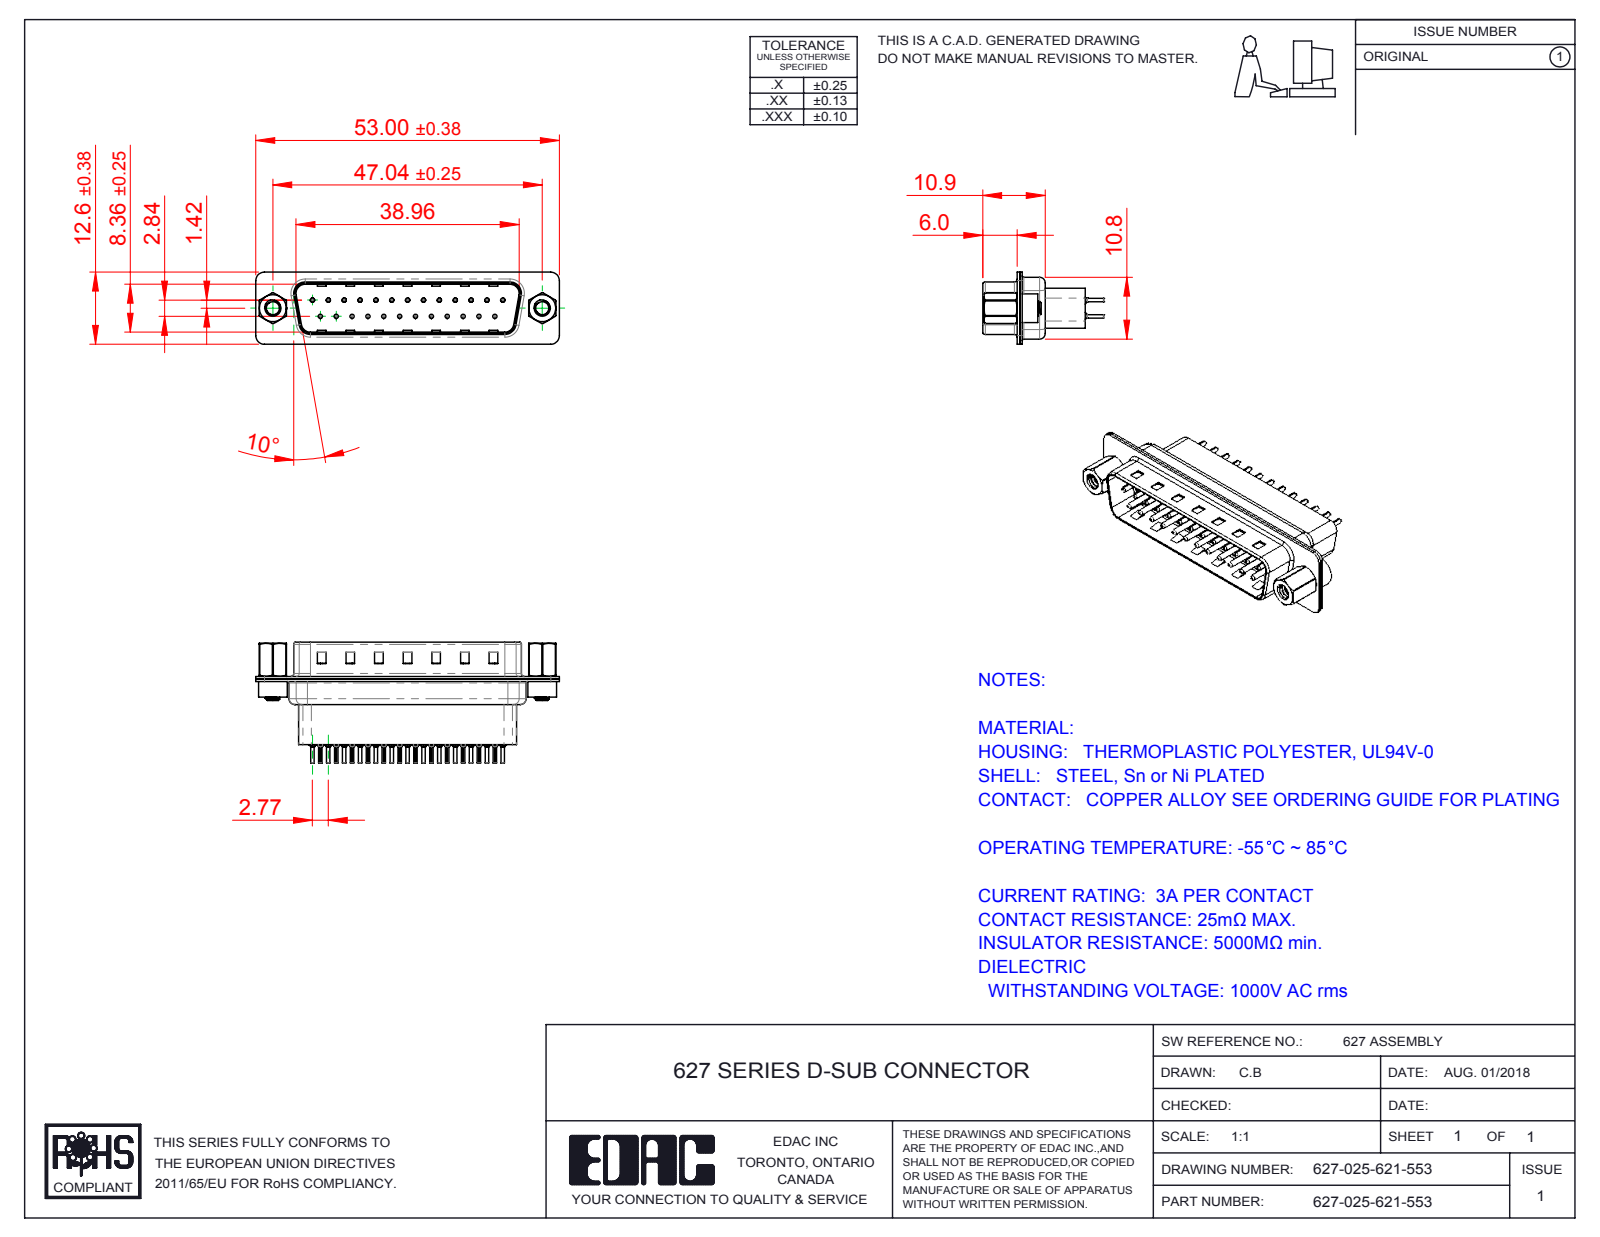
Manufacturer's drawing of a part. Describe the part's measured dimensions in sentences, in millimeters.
The part is named "627 Shell Rear_25 Contacts; 627 Contact Row 1_21H; 627 4-40 Threaded Rivet; 627 Housing_25 HP (+4 more)". Its 3-D file was written by "SolidWorks 2016 (CONFIG_CONTROL_DESIGN)". It is 32 solids with 2952 faces: 793 planar, 1134 cylindrical and 1025 other. Overall it measures 53 by 21.1 by 12.6 millimeters. Its volume is 4 126 cubic millimeters and its surface area 10 464 square millimeters. Round holes: 25 of diameter 0.2, 25 of diameter 0.35, 25 of diameter 1.1, 25 of diameter 1.6, 2 of diameter 2.26, 2 of diameter 2.29, 2 of diameter 4, 2 of diameter 4.8. Round bosses or shafts: 25 of diameter 2, 25 of diameter 1.5, 25 of diameter 0.75, 25 of diameter 0.6, 2 of diameter 5, 2 of diameter 4.9, 2 of diameter 2.79. Partial cylindrical surfaces (rounded edges, fillets, slot ends): 50 of radius 0.1, 16 of radius 1.5, 12 of radius 2, 8 of radius 0.5, 8 of radius 1.6, 4 of radius 0.25, 4 of radius 0.6, 4 of radius 0.65. The main face-to-face distances are 0.4, 0.45, 0.82, 9.58, 0.68, 7.68, 0.9, 1.5, 1.08, 8.08. The hole center spacings are 3.16, 8.31, 2.77, 5.54, 11.08, 16.62, 5.03, 5.04.
